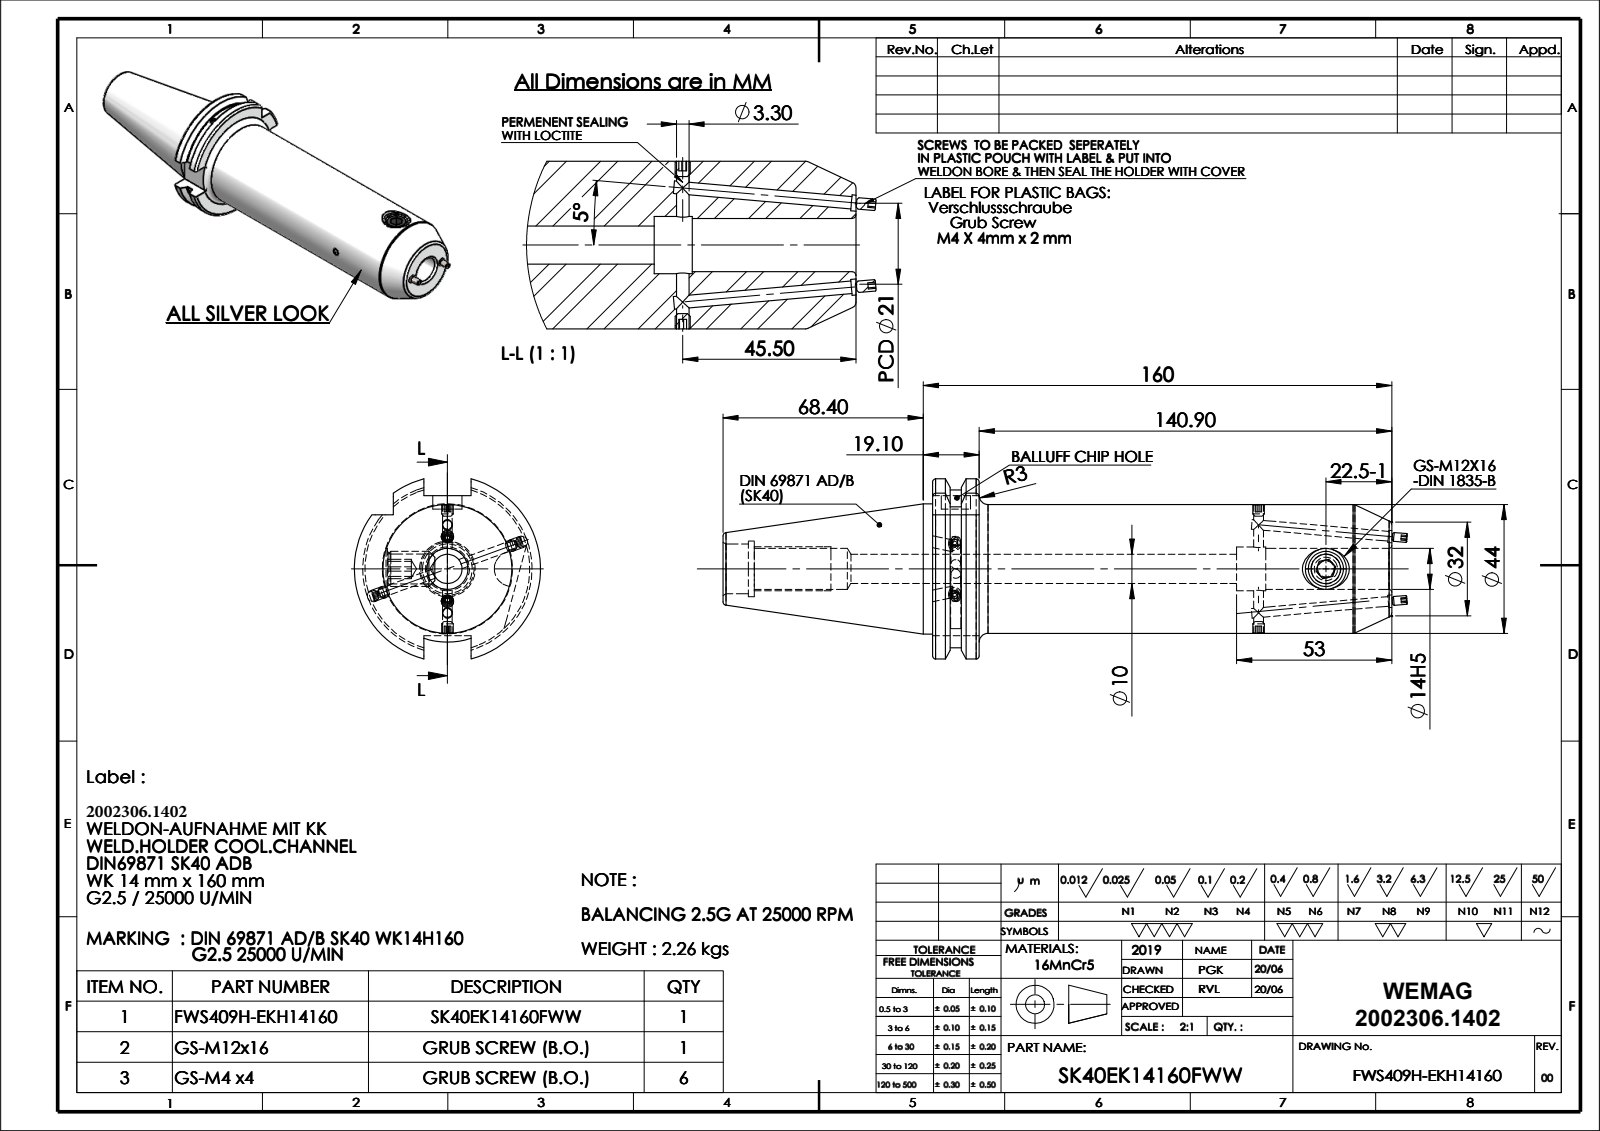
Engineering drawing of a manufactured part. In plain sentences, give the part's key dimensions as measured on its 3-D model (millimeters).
The part is named "91406-WK214160". Its 3-D file was written by "SolidWorks 2018 (CONFIG_CONTROL_DESIGN)". It is 1 solid with 139 faces: 37 planar, 58 cylindrical and 44 other. Overall it measures 228.4 by 63.55 by 61.48 millimeters. Its volume is 293 151 cubic millimeters and its surface area 46 139 square millimeters. Round holes: 4 of diameter 3.3, 2 of diameter 4.2, 2 of diameter 10, 2 of diameter 14, 1 of diameter 10.2, 1 of diameter 15, 1 of diameter 17, 1 of diameter 19. Round bosses or shafts: 1 of diameter 44.45, 1 of diameter 44. Partial cylindrical surfaces (rounded edges, fillets, slot ends): 1 of radius 28.12, 1 of radius 31.77. The main face-to-face distances are 15.9, 156.8, 140.9, 16.1, 47.8, 71.6, 87.5, 228.4, 10.7, 60.9. The hole center spacings are 103.35.
